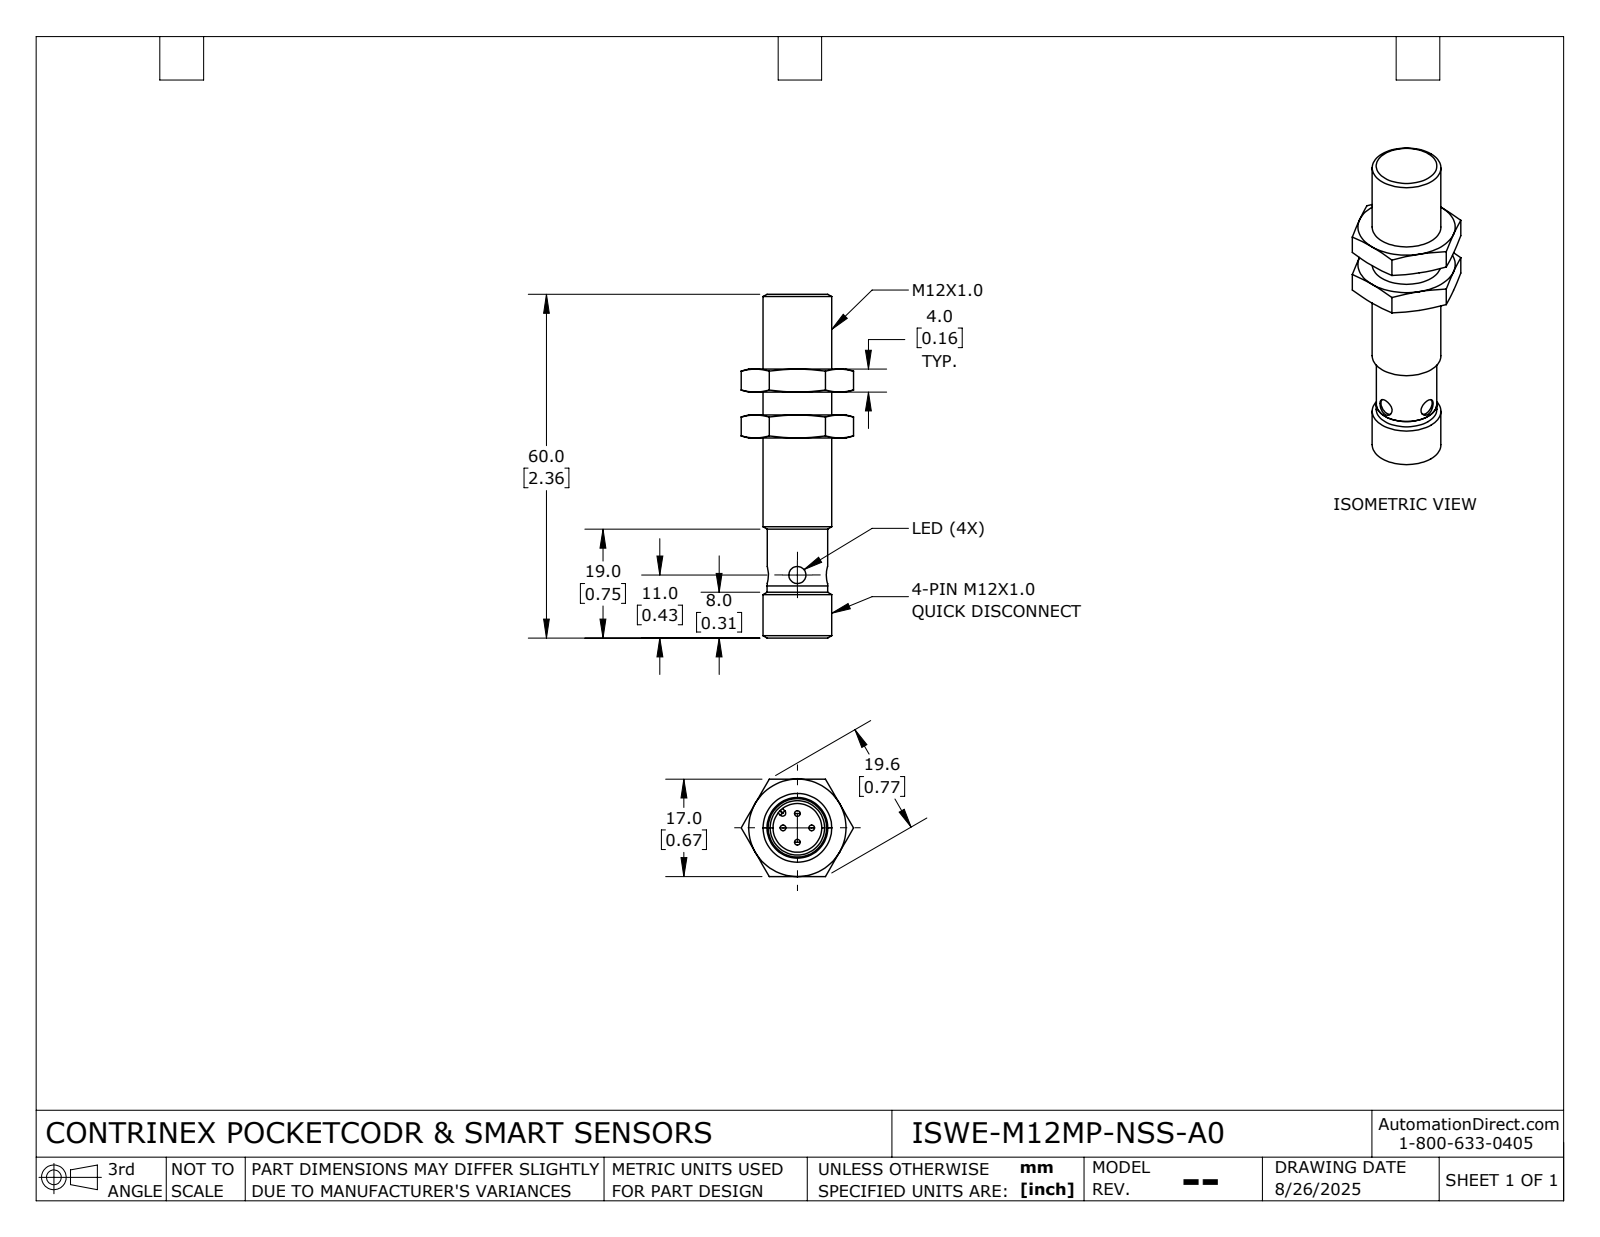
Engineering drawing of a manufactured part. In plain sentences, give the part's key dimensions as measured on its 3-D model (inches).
The part is named "ISWE-M12MP-NSS-A0". Its 3-D file was written by "SolidWorks 2024 (AUTOMOTIVE_DESIGN)". It is 3 solids with 97 faces: 28 planar, 24 cylindrical and 45 other. Overall it measures 2.362 by 0.773 by 0.669 inches. Its volume is 0.443 cubic inches and its surface area 6.288 square inches. Round holes: 1 of diameter 0.118, 1 of diameter 0.118, 1 of diameter 0.335, 1 of diameter 0.43. Round bosses or shafts: 4 of diameter 0.039, 1 of diameter 0.472, 1 of diameter 0.417, 1 of diameter 0.415. Partial cylindrical surfaces (rounded edges, fillets, slot ends): 2 of radius 0.02, 1 of radius 0.022. The main face-to-face distances are 0.157, 0.315, 0.669, 0.472, 0.515, 0.672, 0.83, 0.987, 1.533, 1.375.
